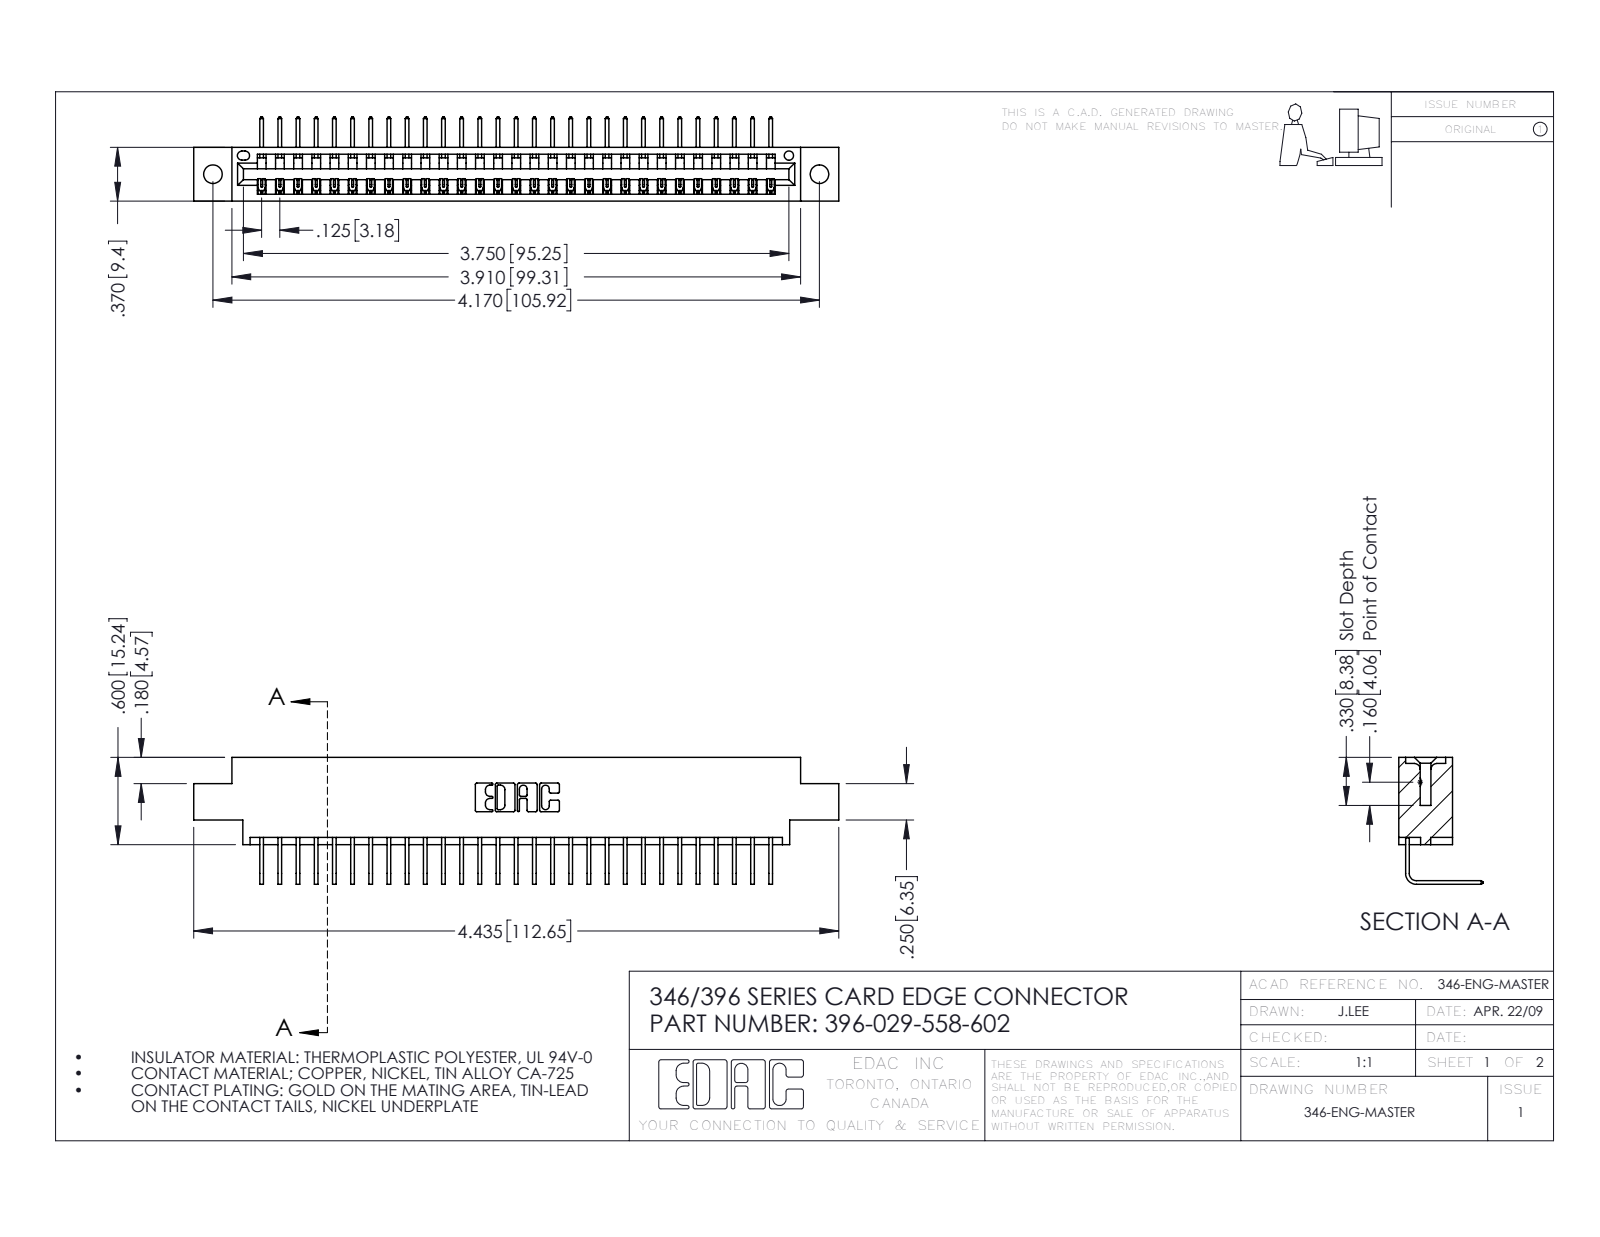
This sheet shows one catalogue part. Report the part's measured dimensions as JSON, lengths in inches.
{"part_name": "346 Part_0.170 Offset - 0.128 Dia; 345-292-001_558 Tail - 2; 396-029-558-602", "step_written_by": "SolidWorks 2016 (CONFIG_CONTROL_DESIGN)", "units": "inches", "bodies": {"solids": 30, "faces": 1866, "planar": 1298, "cylindrical": 568, "other": 0}, "overall_size": [4.435, 0.873, 0.58], "volume_in3": 0.647, "surface_area_in2": 21.04, "round_holes": [[0.128, 2], [0.064, 1]], "partial_cylinders_radius": [[0.006, 58], [0.01, 22], [0.007, 6], [0.031, 6], [0.026, 3], [0.031, 2], [0.04, 2], [0.014, 1]], "face_to_face_distances": [0.322, 0.048, 0.37, 0.25, 0.298, 0.025, 0.072, 0.148, 0.222, 0.1], "hole_center_spacings": [0.246, 3.962, 4.17]}
